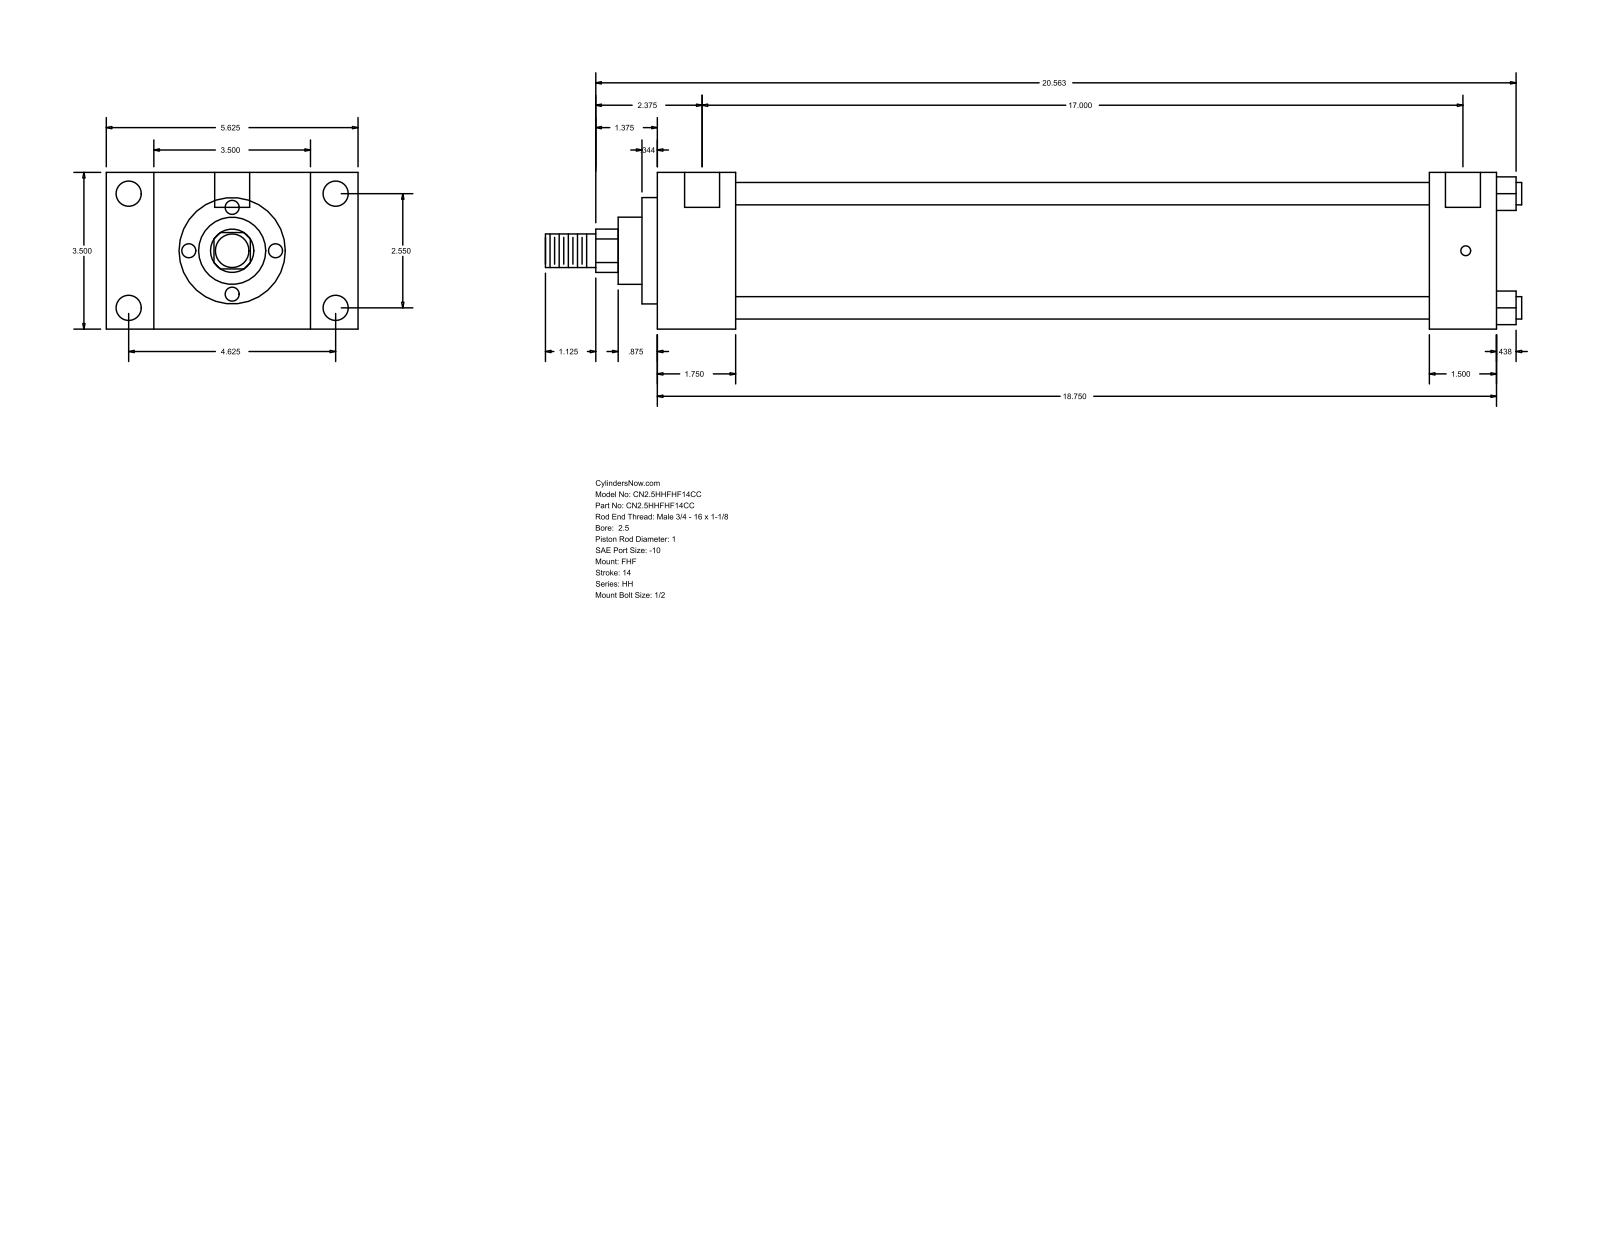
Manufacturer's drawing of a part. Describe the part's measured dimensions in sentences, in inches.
The part is named "HH_FHF__0250_1". Its 3-D file was written by "GSSL Pune (CONFIG_CONTROL_DESIGN)". It is 0 solids with 90 faces: 61 planar, 29 cylindrical and 0 other. Overall it measures 21.813 by 5.625 by 3.5 inches. Round holes: 4 of diameter 0.219, 4 of diameter 0.563, 2 of diameter 0.781. Round bosses or shafts: 4 of diameter 0.5, 1 of diameter 2.875, 1 of diameter 2.375, 1 of diameter 1.5, 1 of diameter 1, 1 of diameter 0.75. Partial cylindrical surfaces (rounded edges, fillets, slot ends): 1 of radius 0.484. The main face-to-face distances are 3.5, 1.75, 1.063, 4.563, 18.75, 17, 5.625, 17.25, 15.5, 1.5. The hole center spacings are 0.063, 2.55, 4.625, 5.281, 17.062, 17.125, 17.
